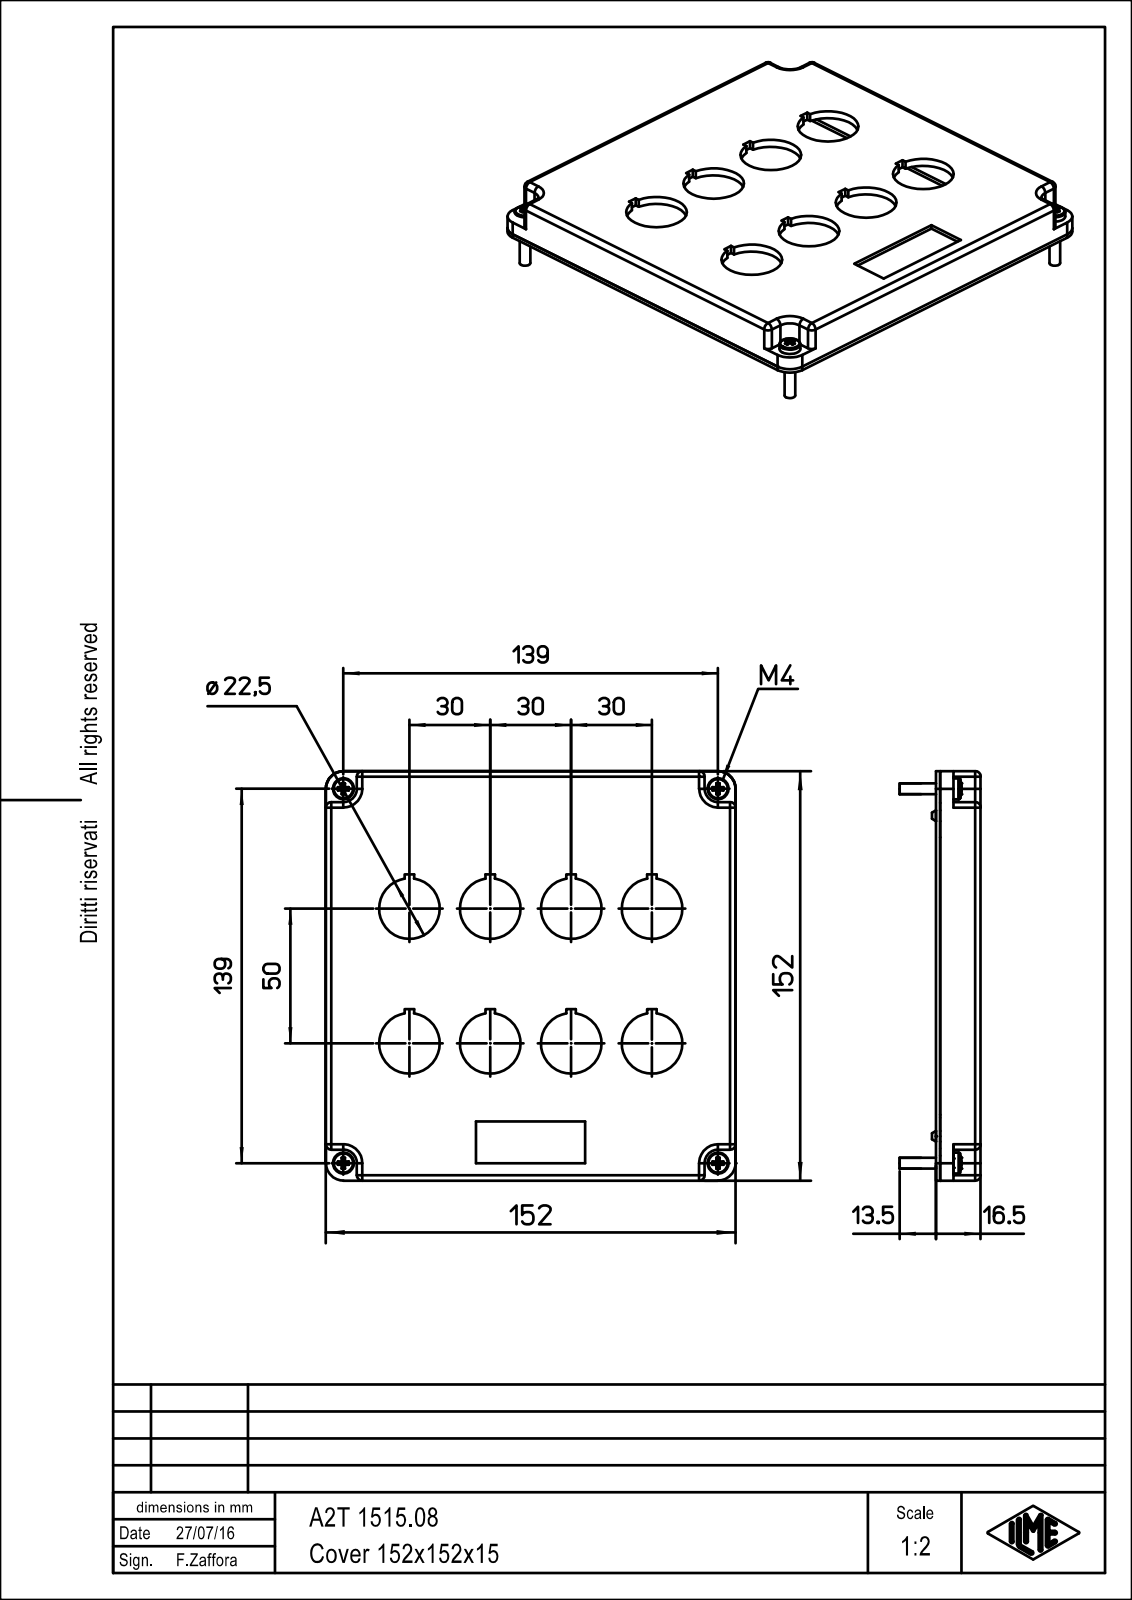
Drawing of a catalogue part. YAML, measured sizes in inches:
part_name: "A2T_1515.08"
step_written_by: "PTC Creo Elements/Direct Modeling 19.0B 21-Mar-2015 (C) Parametric Technology GmbH (AUTOMOTIVE_DESIGN)"
units: inches
bodies: {solids: 1, faces: 598, planar: 450, cylindrical: 112, other: 36}
overall_size: [5.985, 5.984, 1.181]
volume: 5.814
surface_area: 107.9
round_holes:
  - {diameter: 0.886, count: 8}
  - {diameter: 0.177, count: 4}
  - {diameter: 0.13, count: 1}
  - {diameter: 0.228, count: 1}
round_bosses_or_shafts:
  - {diameter: 0.307, count: 4}
  - {diameter: 0.157, count: 4}
  - {diameter: 0.236, count: 2}
  - {diameter: 0.276, count: 1}
  - {diameter: 0.244, count: 1}
partial_cylinders:
  - {radius: 0.079, count: 17}
  - {radius: 0.013, count: 11}
  - {radius: 0.256, count: 8}
  - {radius: 0.197, count: 6}
  - {radius: 0.315, count: 6}
  - {radius: 0.011, count: 2}
  - {radius: 0.011, count: 2}
  - {radius: 0.007, count: 1}
face_to_face_distances: [0.118, 0.531, 0.65, 5.866, 0.059, 0.472, 0.591, 5.984, 5.748, 0.335]
hole_center_spacings: [1.181, 2.296, 1.969, 2, 2.362, 2.77, 3.075, 3.76]
